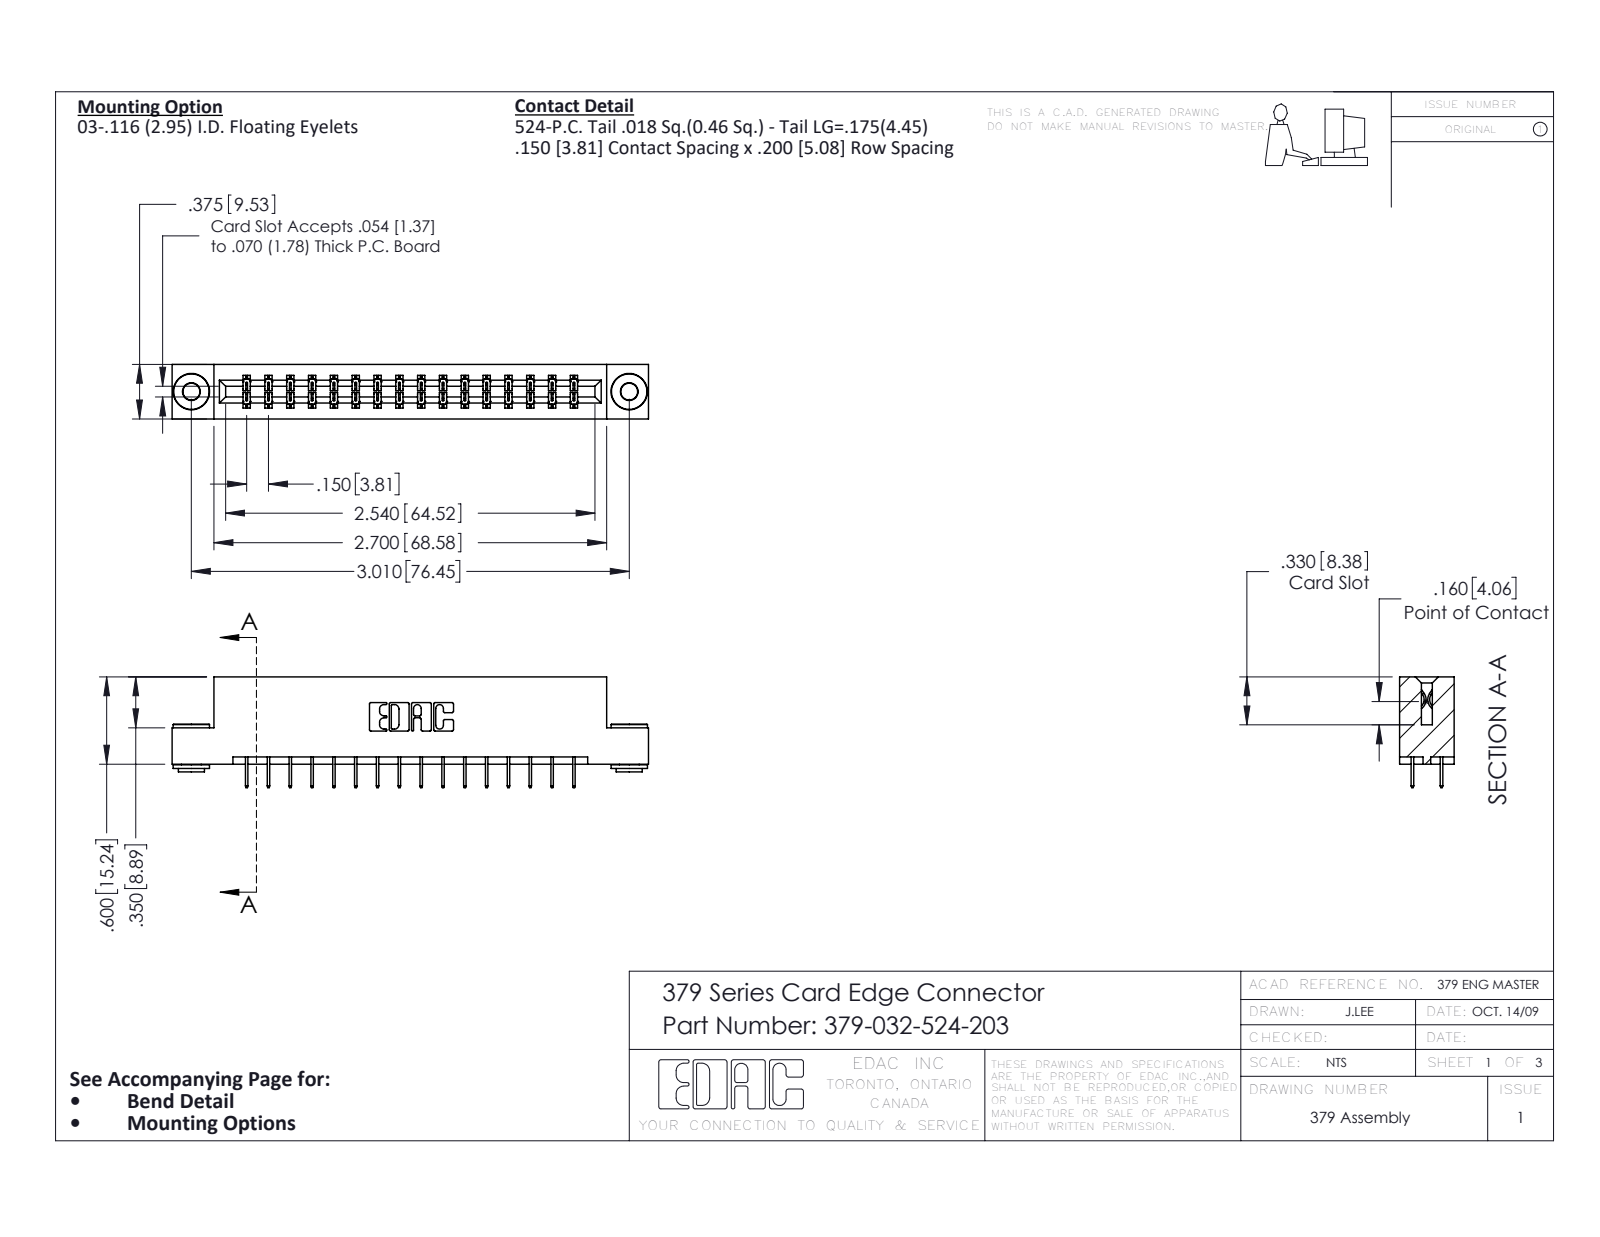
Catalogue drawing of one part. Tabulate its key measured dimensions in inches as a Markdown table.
| quantity | value |
| --- | --- |
| part name | 345-292-001_345-293-124; 345-250-002_345-250-002-102; 379-032-524-203; 379 Part_Flush - .156 Dia - TH |
| STEP written by | SolidWorks 2020 (CONFIG_CONTROL_DESIGN) |
| units | inches |
| bodies | 35 solids, 1944 faces (1424 planar, 512 cylindrical, 8 other) |
| overall size | 3.275 × 0.762 × 0.375 |
| volume | 0.519 in³ |
| surface area | 14.55 in² |
| round holes (diameter × count) | 0.116 × 2, 0.156 × 2 |
| round bosses / shafts (diameter × count) | 0.25 × 2, 0.18 × 2, 0.136 × 2 |
| partial cylindrical surfaces (radius × count) | 0.006 × 63, 0.01 × 22, 0.007 × 6, 0.031 × 6, 0.026 × 3, 0.014 × 2, 0.022 × 2, 0.024 × 2 |
| main face-to-face distances | 0.3, 0.375, 0.2, 0.075, 0.1, 0.15, 0.05, 0.6, 0.225, 0.55 |
| hole center spacings | 3.01 |
